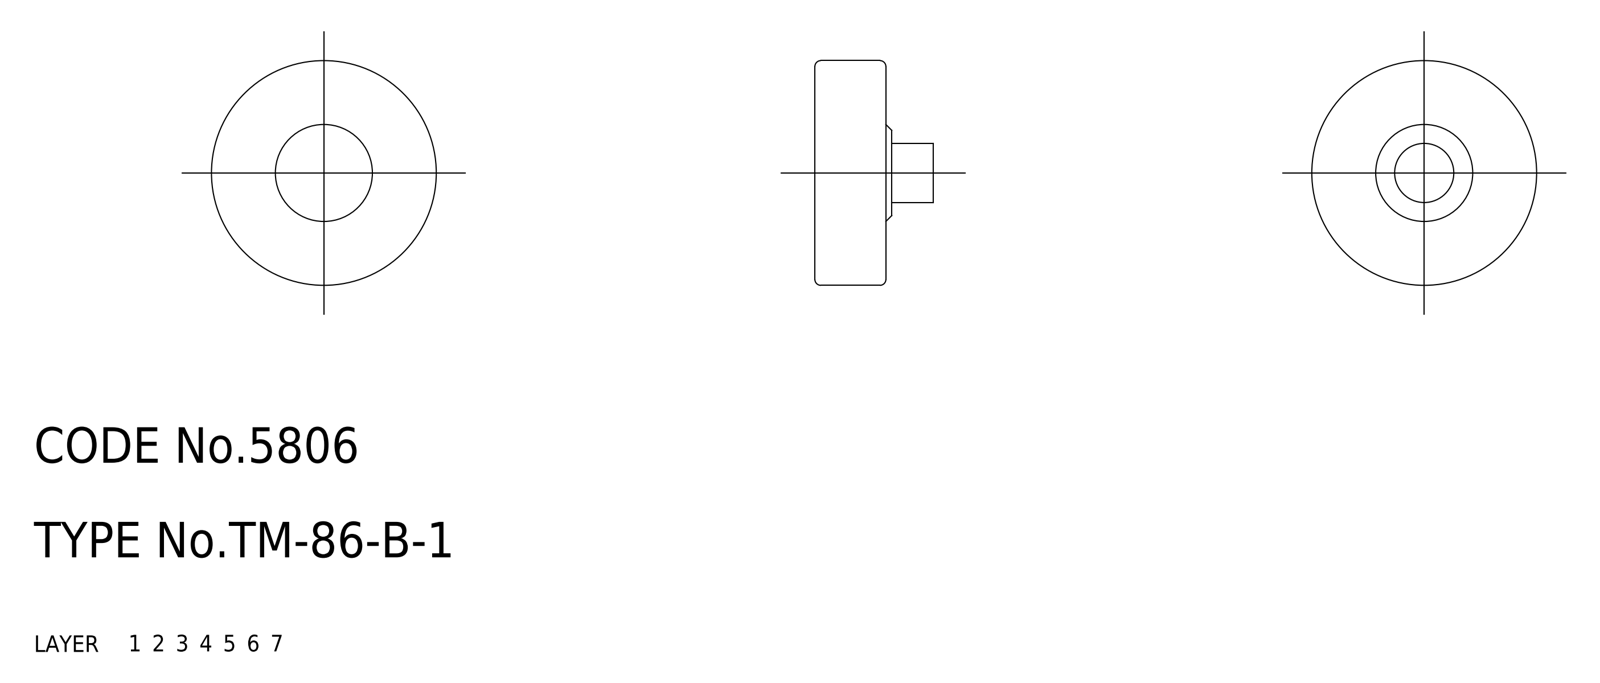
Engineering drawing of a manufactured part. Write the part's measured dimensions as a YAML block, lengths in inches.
part_name: "roller"
step_written_by: "CADfix (AUTOMOTIVE_DESIGN)"
units: inches
bodies: {solids: 1, faces: 28, planar: 0, cylindrical: 0, other: 28}
overall_size: [0.748, 0.748, 0.394]
volume: 0.109
surface_area: 2.085
